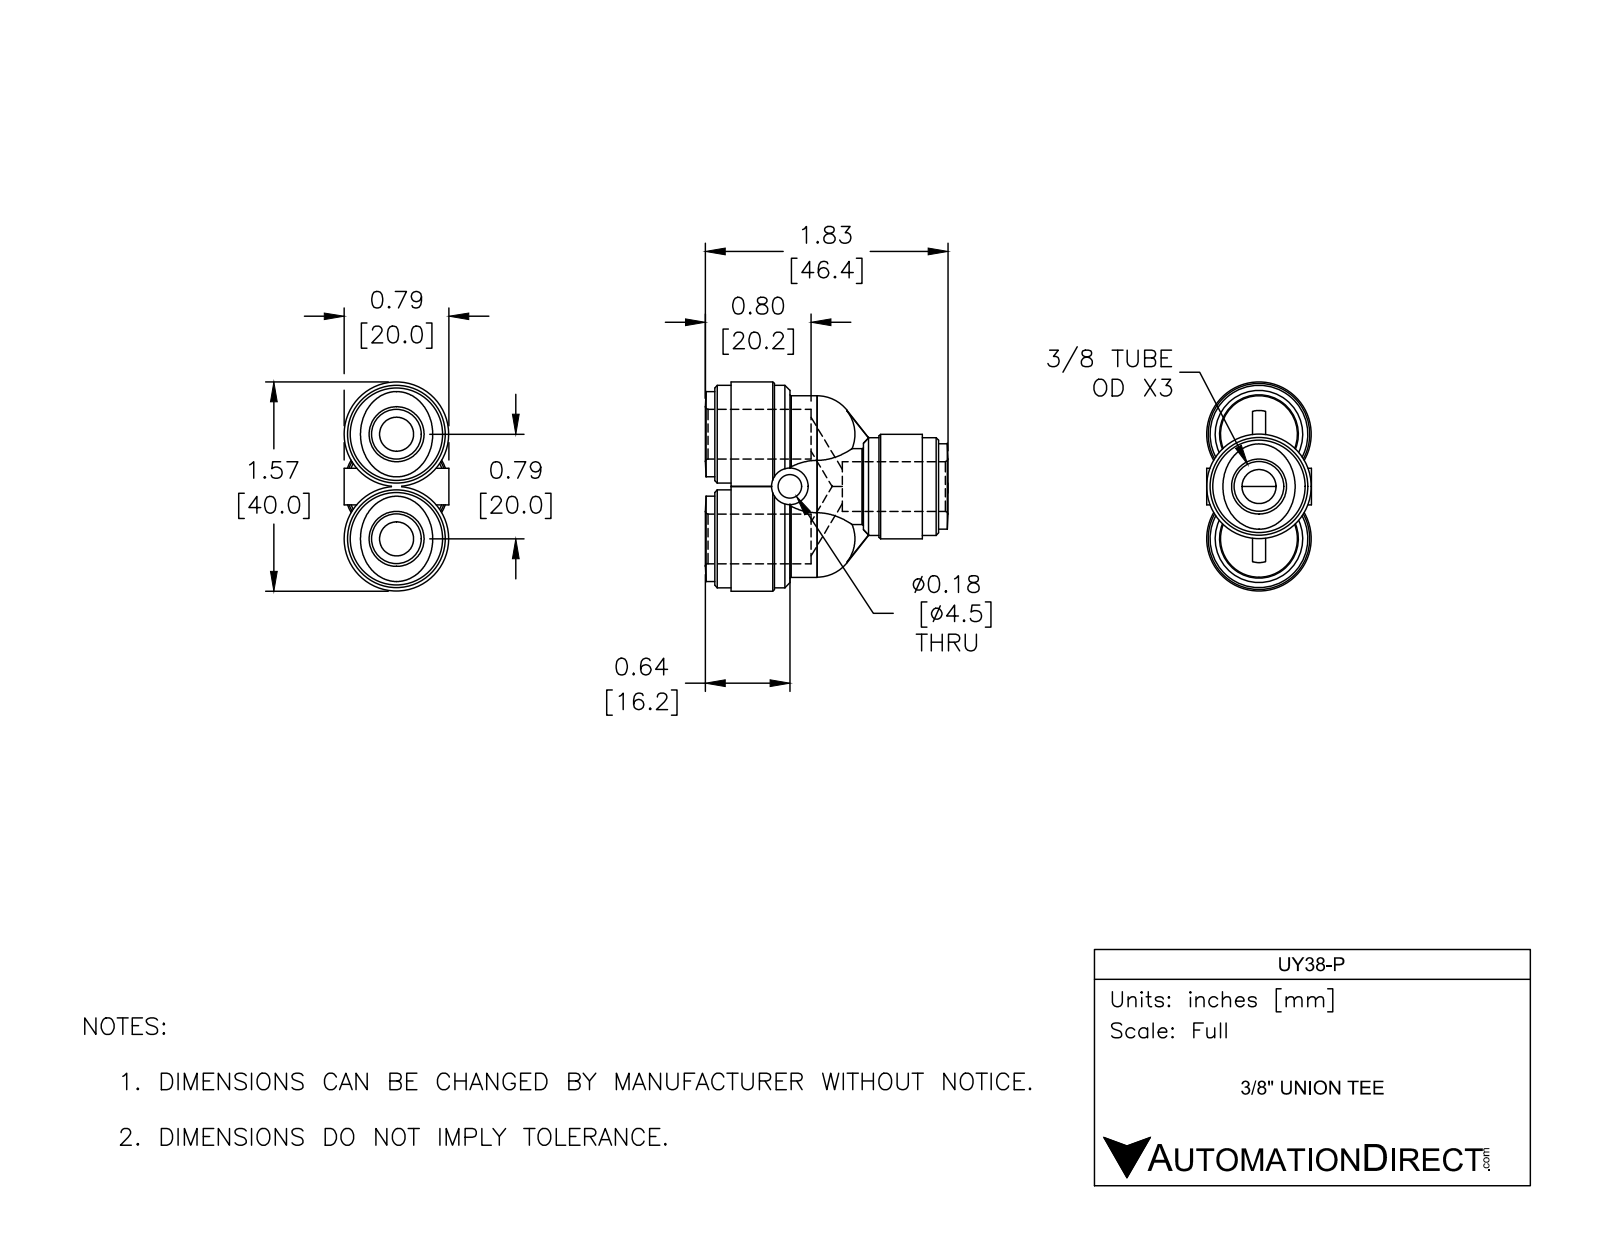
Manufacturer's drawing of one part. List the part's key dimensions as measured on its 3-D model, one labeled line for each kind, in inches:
Part name (STEP PRODUCT): UY38-P
STEP written by: SolidWorks 2017 (AUTOMOTIVE_DESIGN)
Units: inches
Bodies: 1 solid, 123 faces (23 planar, 40 cylindrical, 60 other)
Overall size (bounding box): 1.827 × 1.575 × 0.787
Volume: 0.866 in³ · Surface area: 11.89 in²
Round holes (diameter × count): ⌀0.374 ×3, ⌀0.177 ×1
Round bosses / shafts (diameter × count): ⌀0.787 ×3, ⌀0.736 ×3, ⌀0.579 ×3, ⌀0.276 ×1
Main face-to-face distances: 0.122, 0.724, 0.602, 1.563, 0.961, 0.567, 1.118, 0.445, 0.157, 0.839
Hole centre spacings: 0.394, 0.787
